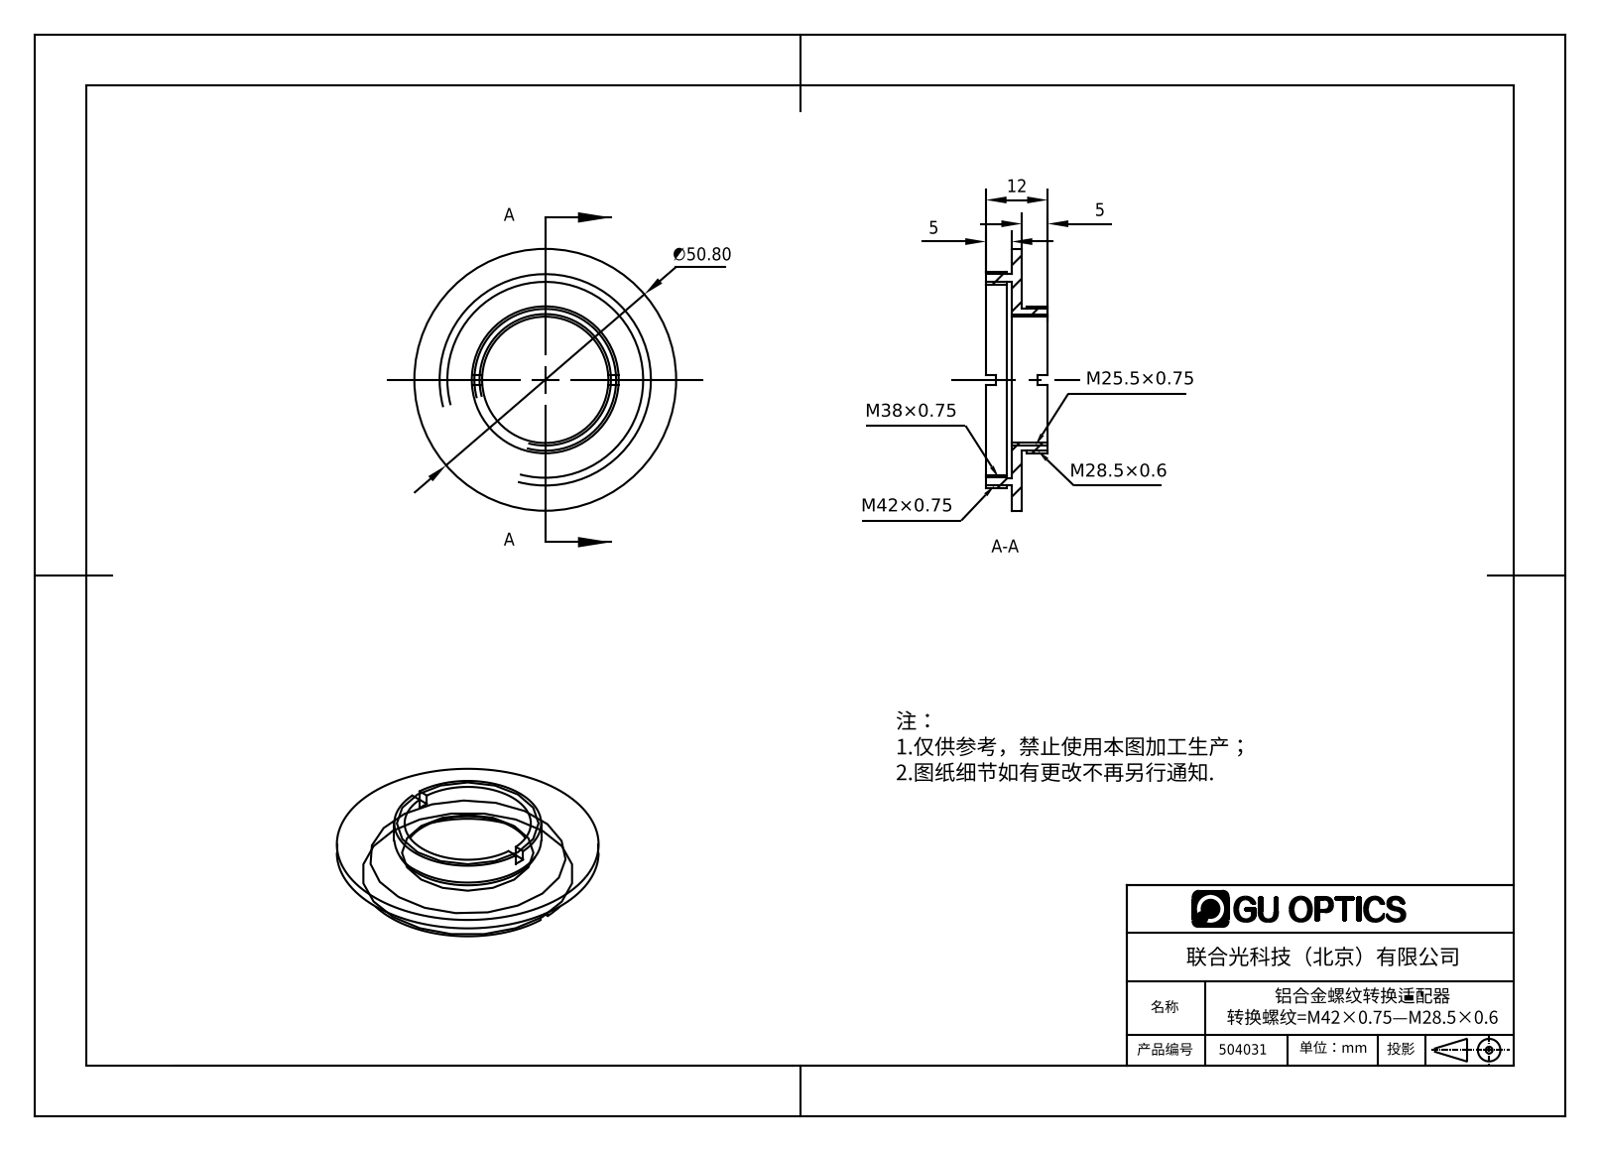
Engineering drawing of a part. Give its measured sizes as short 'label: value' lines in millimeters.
name: 504031
written by: SolidWorks 2016 (AUTOMOTIVE_DESIGN)
unit: mm
bodies: 1 solid, 38 faces (22 planar, 16 cylindrical, 0 other)
size: 50.8 × 50.8 × 12
volume: 5 278 mm³; area: 6 019 mm²
holes: 1× ⌀24.5, 1× ⌀37, 1× ⌀38.2
bosses: 1× ⌀50.8, 1× ⌀42, 1× ⌀41, 1× ⌀28.5, 1× ⌀27.5
face distances: 2, 5, 7, 4, 3, 8, 1, 12, 10, 6
